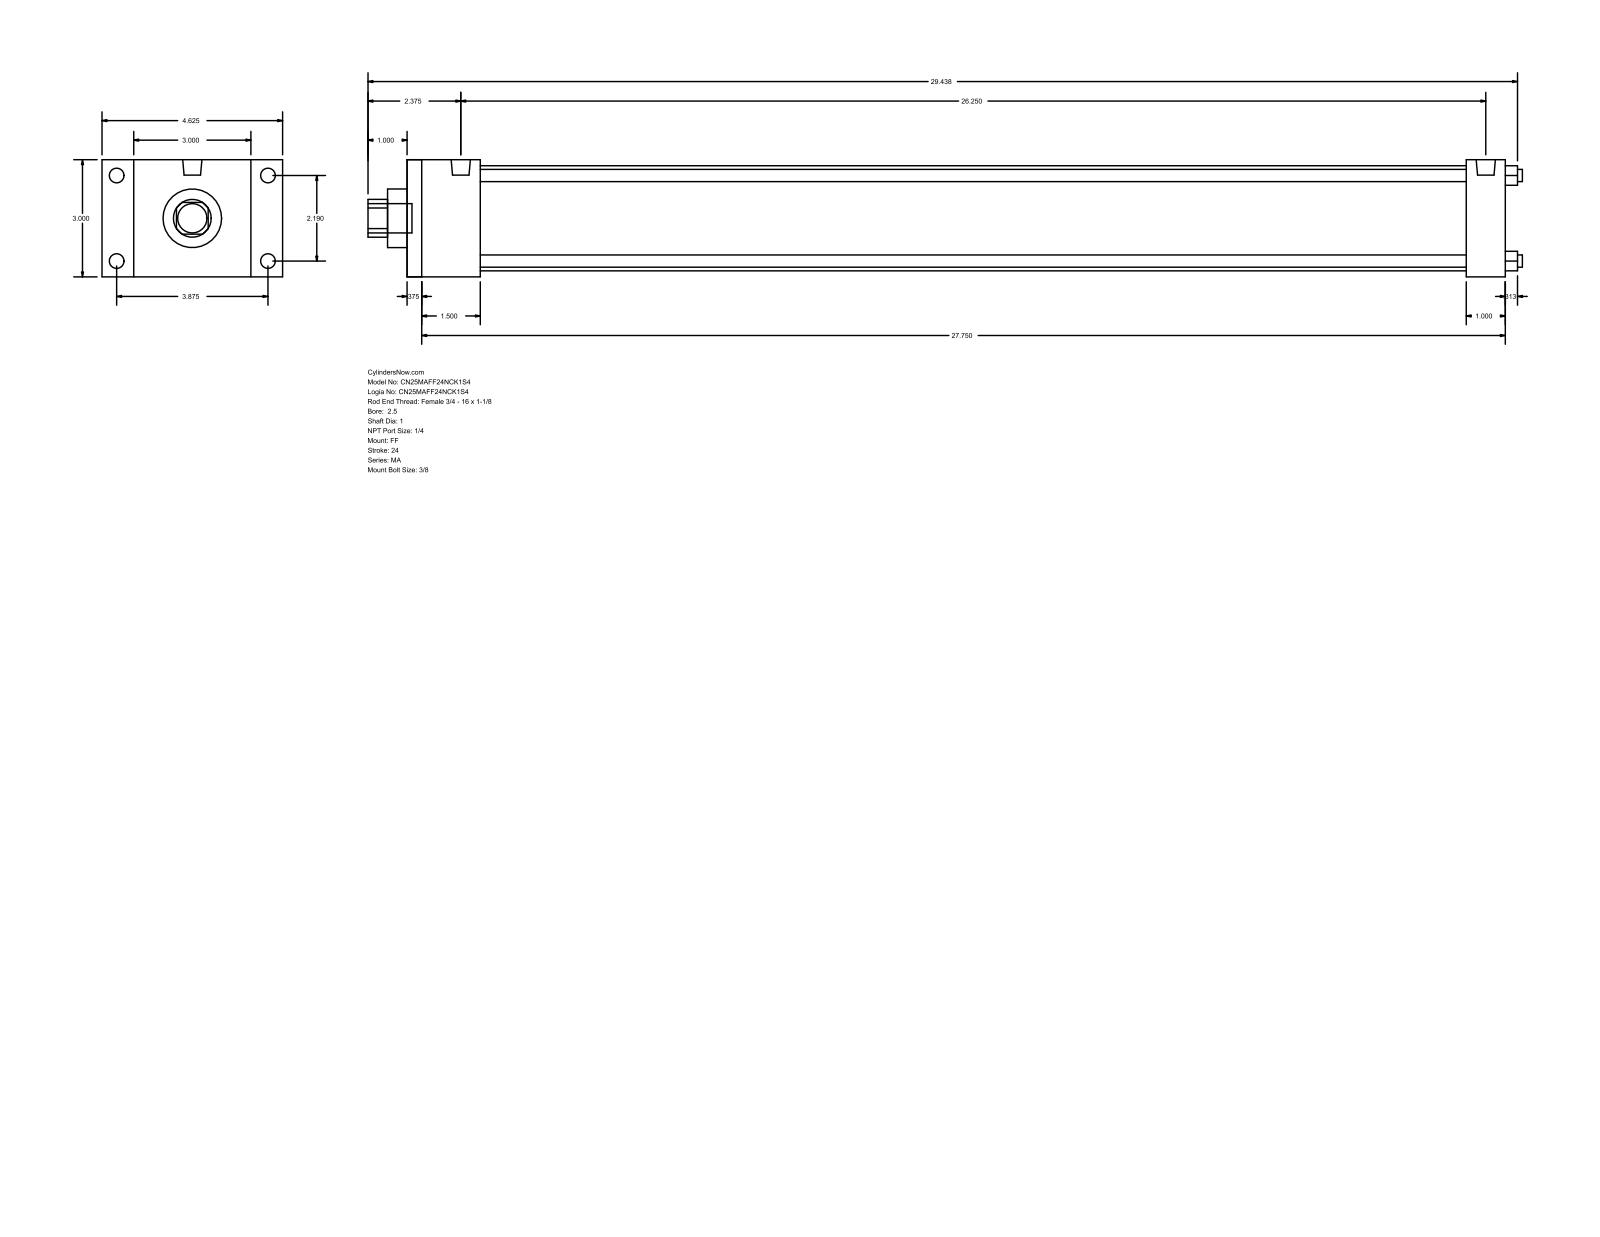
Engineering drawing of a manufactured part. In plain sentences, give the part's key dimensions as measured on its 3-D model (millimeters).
The part is named "MA_FF__0250_1". Its 3-D file was written by "GSSL Pune (CONFIG_CONTROL_DESIGN)". It is 0 solids with 92 faces: 64 planar, 28 cylindrical and 0 other. Overall it measures 750.89 by 117.47 by 76.2 millimeters. Round holes: 4 of diameter 7.94, 1 of diameter 25.4, 1 of diameter 38.1, 1 of diameter 68.33. Round bosses or shafts: 4 of diameter 9.53, 4 of diameter 7.94, 2 of diameter 12.49, 1 of diameter 19.05. Partial cylindrical surfaces (rounded edges, fillets, slot ends): 1 of radius 12.29. The main face-to-face distances are 76.2, 714.37, 704.85, 9.52, 25.39, 47.63, 688.98, 38.11, 679.46, 641.35. The hole center spacings are 39.33, 55.62, 78.66.
